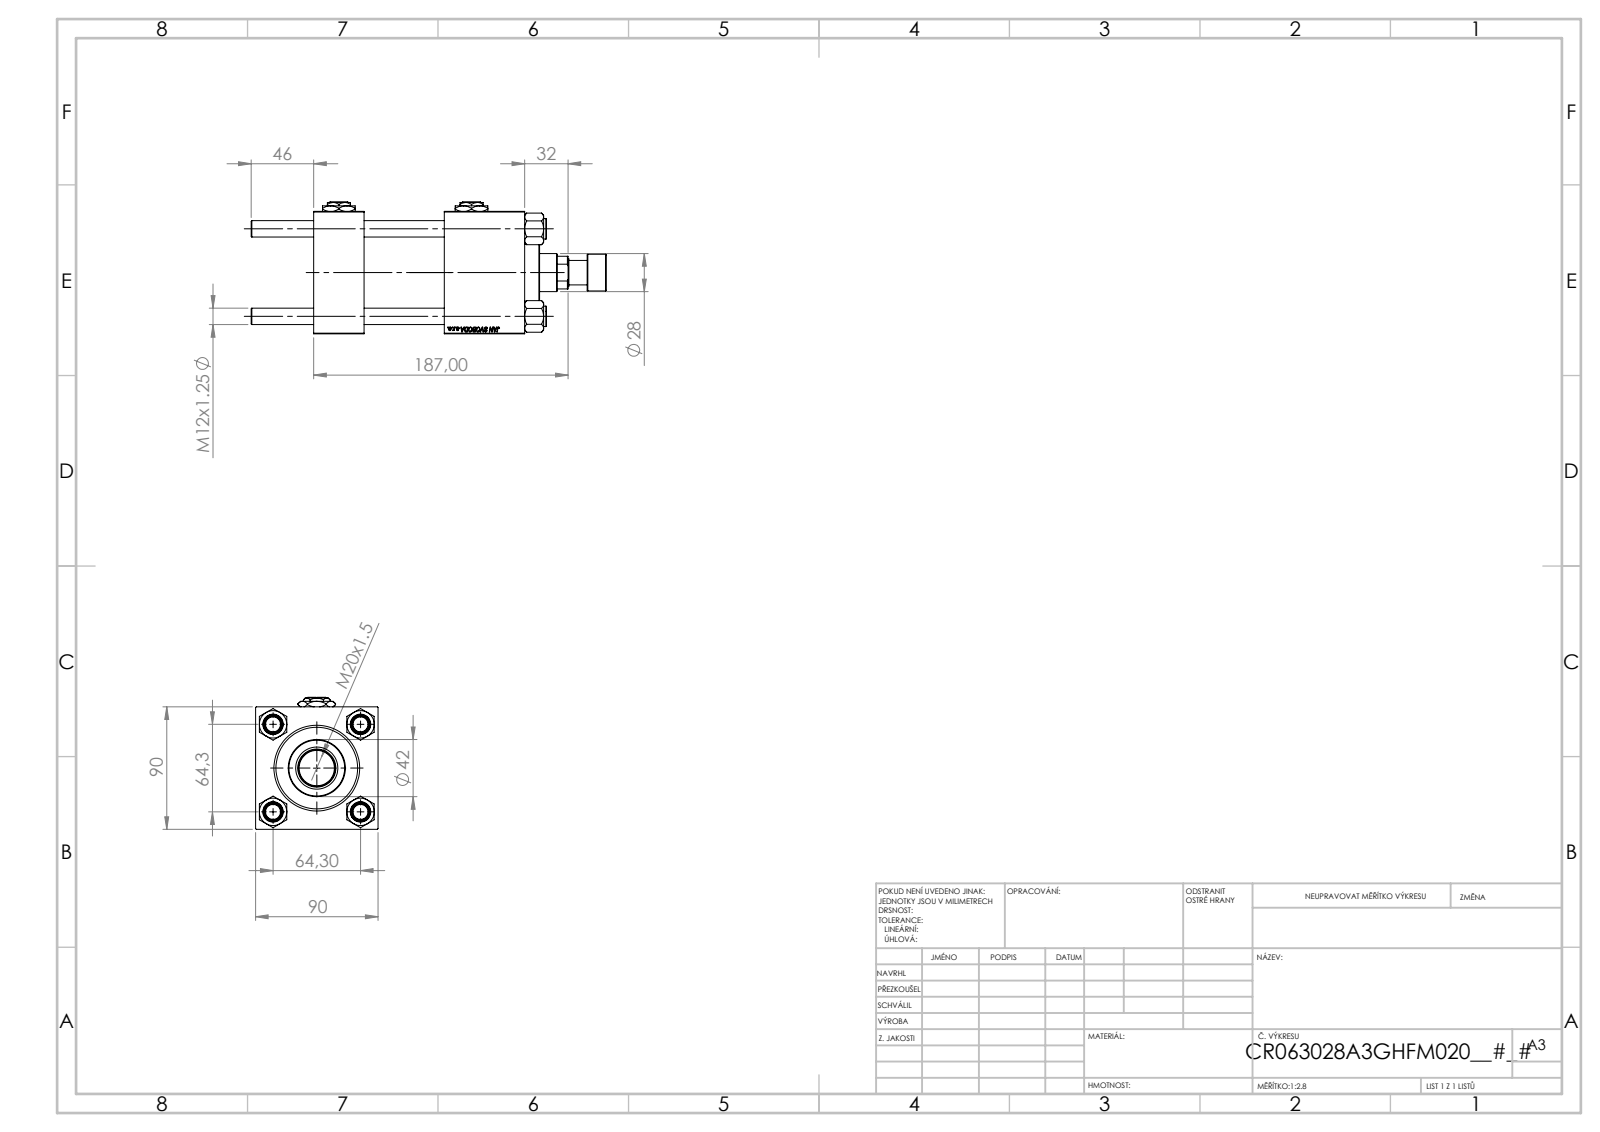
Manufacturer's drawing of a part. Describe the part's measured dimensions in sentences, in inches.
The part is named "V215CR_BODY_A; NUT_M5; Zatka_pro_OIL_PORT; V215CR_ROD_END_F (+3 more)". Its 3-D file was written by "SolidWorks 2019 (CONFIG_CONTROL_DESIGN)". It is 14 solids with 1247 faces: 571 planar, 92 cylindrical and 584 other. Overall it measures 10.276 by 3.819 by 3.543 inches. Its volume is 60.2 cubic inches and its surface area 315.1 square inches. Round holes: 4 of diameter 0.472, 2 of diameter 0.276, 2 of diameter 0.825, 2 of diameter 1.181, 1 of diameter 0.728, 1 of diameter 1.102, 1 of diameter 1.22, 1 of diameter 1.969, 1 of diameter 2.362, 1 of diameter 2.48. Round bosses or shafts: 4 of diameter 0.591, 1 of diameter 2.717, 1 of diameter 1.654, 1 of diameter 1.063, 1 of diameter 0.709. The main face-to-face distances are 3.543, 2.323, 1.457, 6.102, 4.646, 3.78, 4.972, 3.516, 1.193, 1.13. The hole center spacings are 1.79, 2.531, 3.58, 3.839.
